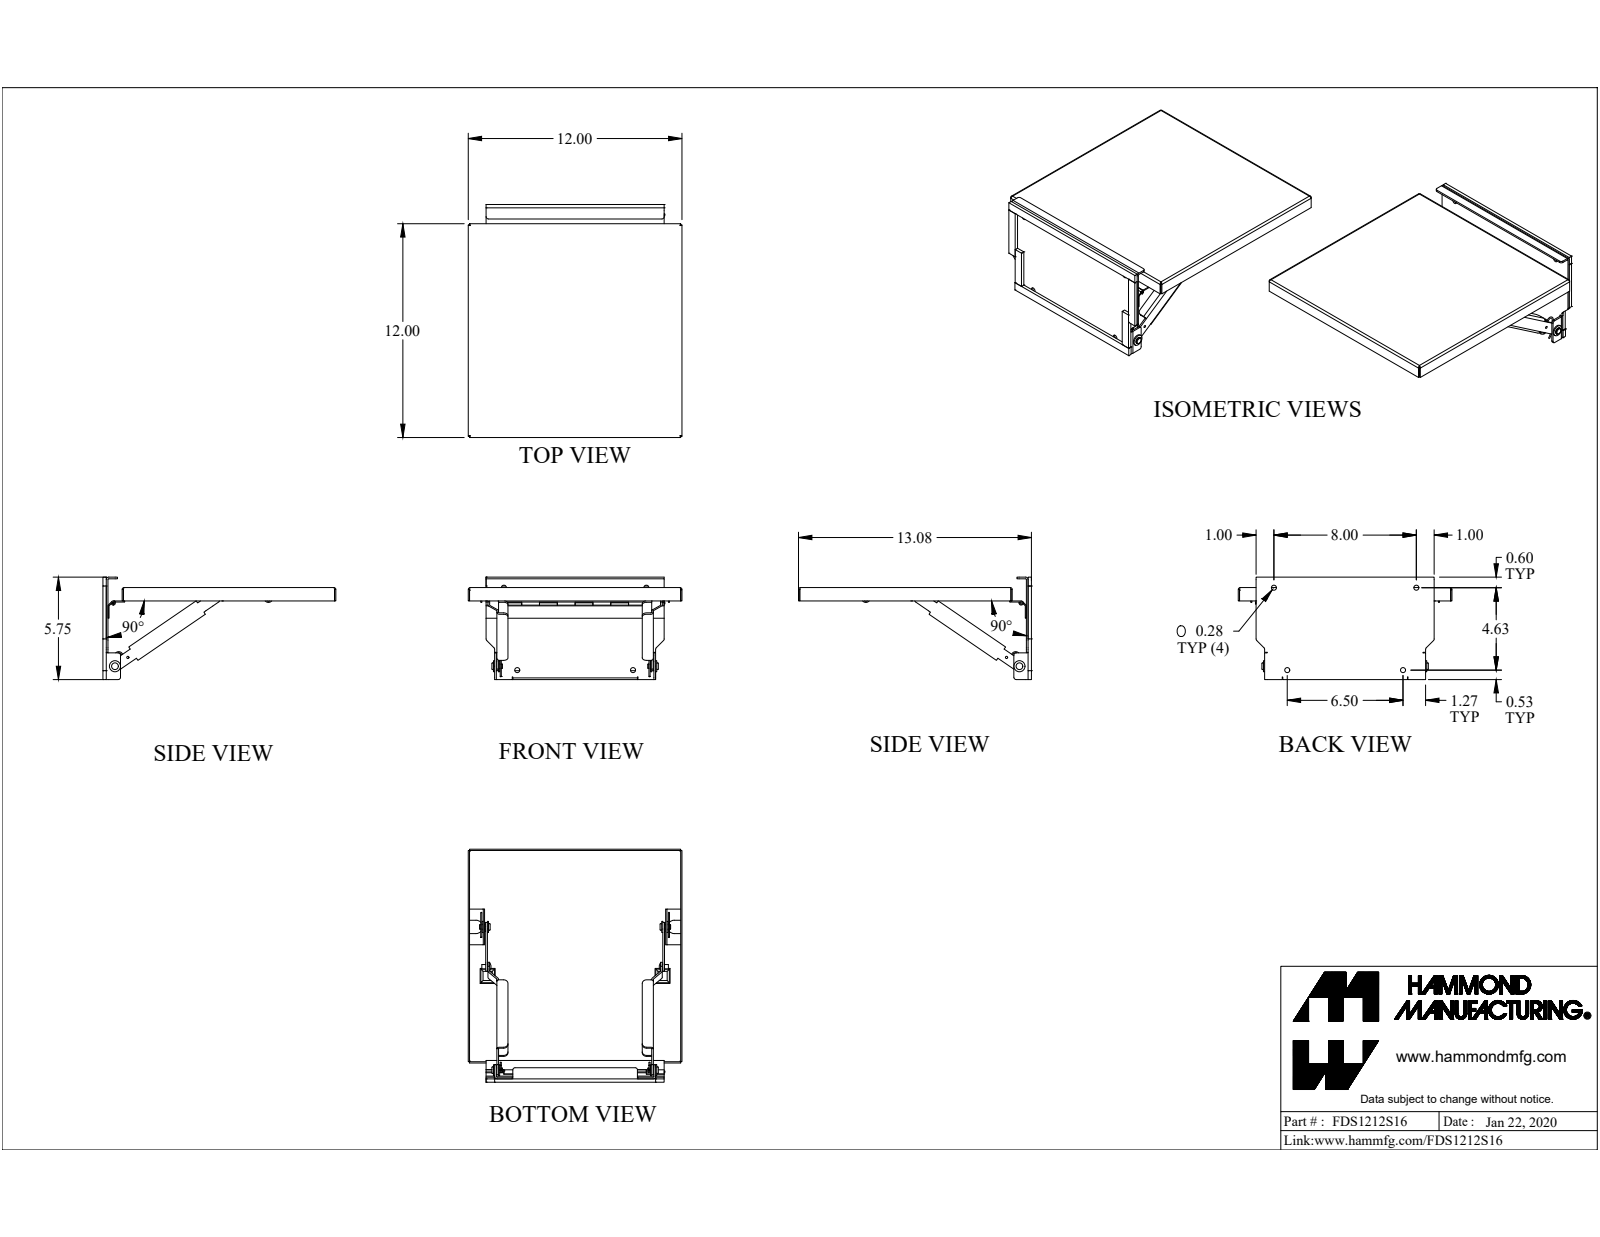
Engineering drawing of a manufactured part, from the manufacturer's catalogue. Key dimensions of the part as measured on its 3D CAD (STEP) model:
Part name (STEP PRODUCT): FDS1212S16
STEP written by: SolidWorks 2019 (CONFIG_CONTROL_DESIGN)
Units: inches
Bodies: 42 solids, 588 faces (363 planar, 176 cylindrical, 49 other)
Overall size (bounding box): 13.079 × 12 × 5.75
Volume: 26.62 in³ · Surface area: 684.8 in²
Round holes (diameter × count): ⌀0.094 ×4, ⌀0.281 ×4, ⌀0.125 ×3, ⌀0.265 ×3, ⌀0.257 ×2, ⌀0.26 ×2, ⌀0.282 ×2, ⌀0.11 ×1
Round bosses / shafts (diameter × count): ⌀0.25 ×3, ⌀0.625 ×2, ⌀0.51 ×2, ⌀0.375 ×2, ⌀0.625 ×1, ⌀0.5 ×1, ⌀0.234 ×1, ⌀0.1 ×1
Partial cylindrical surfaces — rounded edges, fillets, slot ends (radius × count): R0.25 ×16, R0.048 ×12, R0.143 ×12, R0.125 ×11, R0.036 ×6, R0.108 ×6, R0.375 ×6, R0.05 ×4
Main face-to-face distances: 0.072, 0.095, 11.928, 11.856, 0.095, 12, 0.282, 0.187, 0.062, 0.03
Hole centre spacings: 0.875, 1.322, 4.685, 4.705, 5.341, 7.034, 8.6, 8.994
